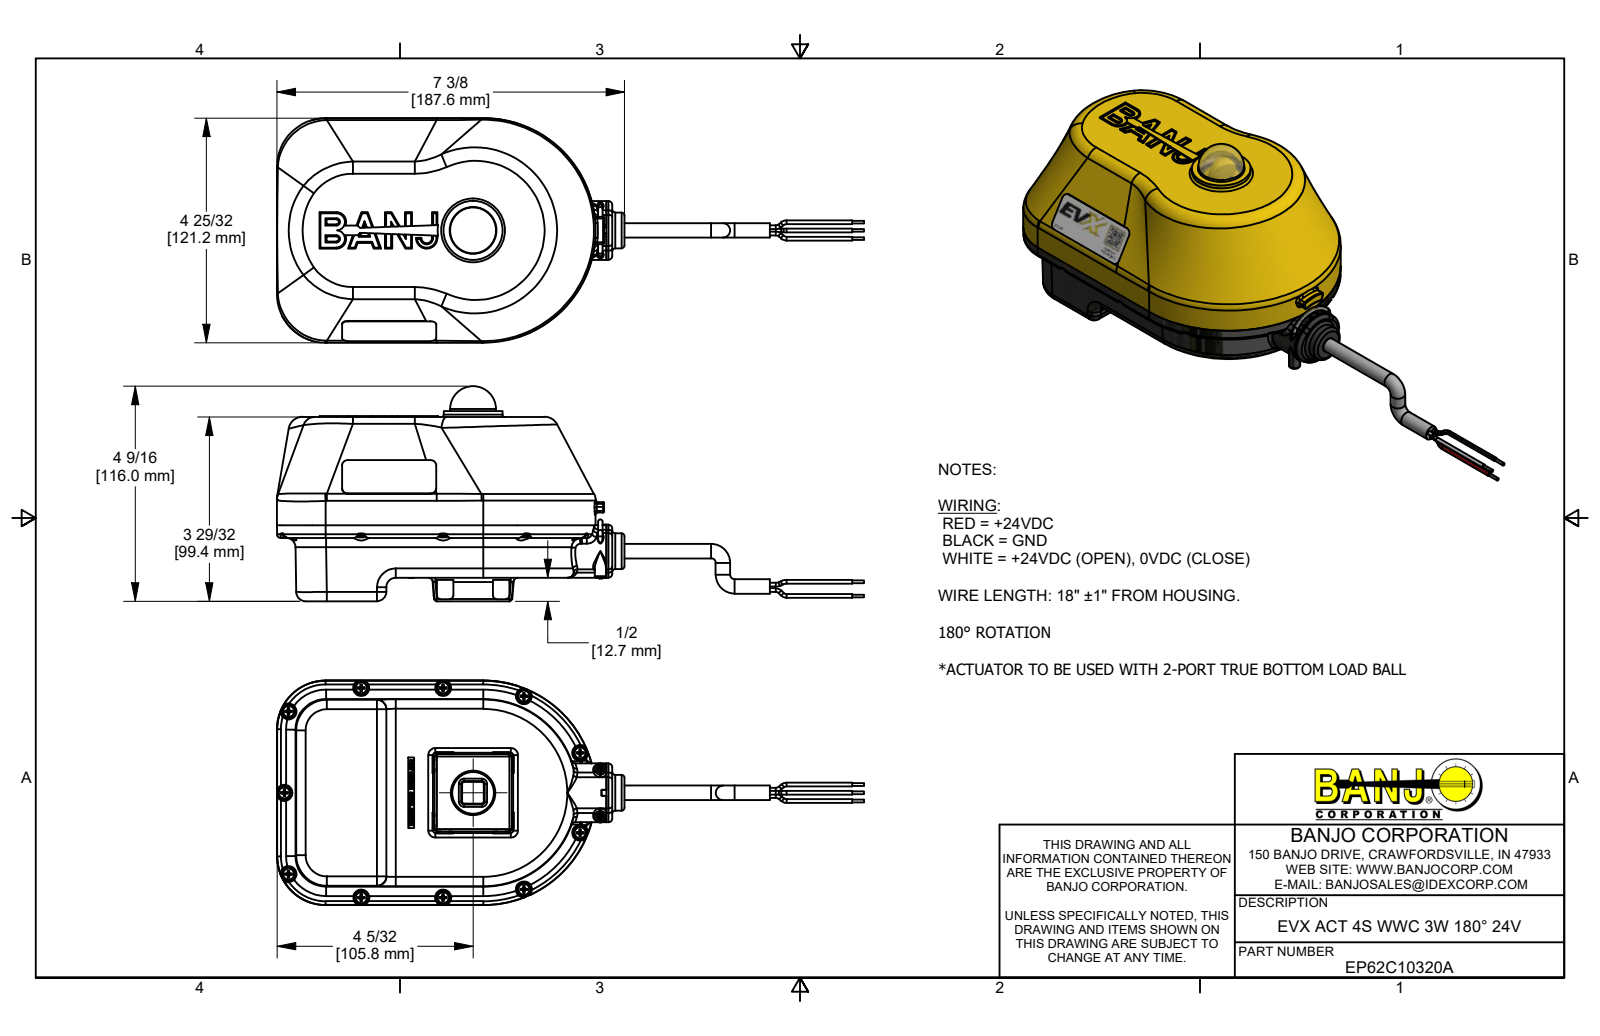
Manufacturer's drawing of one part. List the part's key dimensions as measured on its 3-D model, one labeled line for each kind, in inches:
Part name (STEP PRODUCT): EP62C10320A; B61905PPHS; B632038PM; EP10320A (+8 more)
STEP written by: Autodesk Inventor 2019 (AUTOMOTIVE_DESIGN)
Units: inches
Bodies: 67 solids, 6932 faces (2408 planar, 2950 cylindrical, 1574 other)
Overall size (bounding box): 12.476 × 4.77 × 4.569
Volume: 35.06 in³ · Surface area: 463.2 in²
Round holes (diameter × count): ⌀0.15 ×15, ⌀0.095 ×11, ⌀0.34 ×11, ⌀0.08 ×7, ⌀0.104 ×4, ⌀0.136 ×4, ⌀0.148 ×4, ⌀0.176 ×4, ⌀0.266 ×4, ⌀0.105 ×2, ⌀0.125 ×2, ⌀0.127 ×2
Round bosses / shafts (diameter × count): ⌀0.25 ×19, ⌀0.08 ×15, ⌀0.14 ×11, ⌀0.108 ×11, ⌀0.085 ×11, ⌀0.058 ×6, ⌀0.437 ×4, ⌀0.375 ×4
Partial cylindrical surfaces — rounded edges, fillets, slot ends (radius × count): R0.013 ×204, R0.405 ×138, R0.387 ×114, R0.309 ×112, R0.253 ×108, R0.609 ×106, R0.01 ×100, R0.04 ×46
Main face-to-face distances: 0.083, 0.085, 0.125, 0.181, 0.096, 2.175, 2.271, 2.356, 0.5, 2.3
Hole centre spacings: 1.313, 4.245, 4.287, 0.55, 0.952, 0.954, 0.964, 0.998
